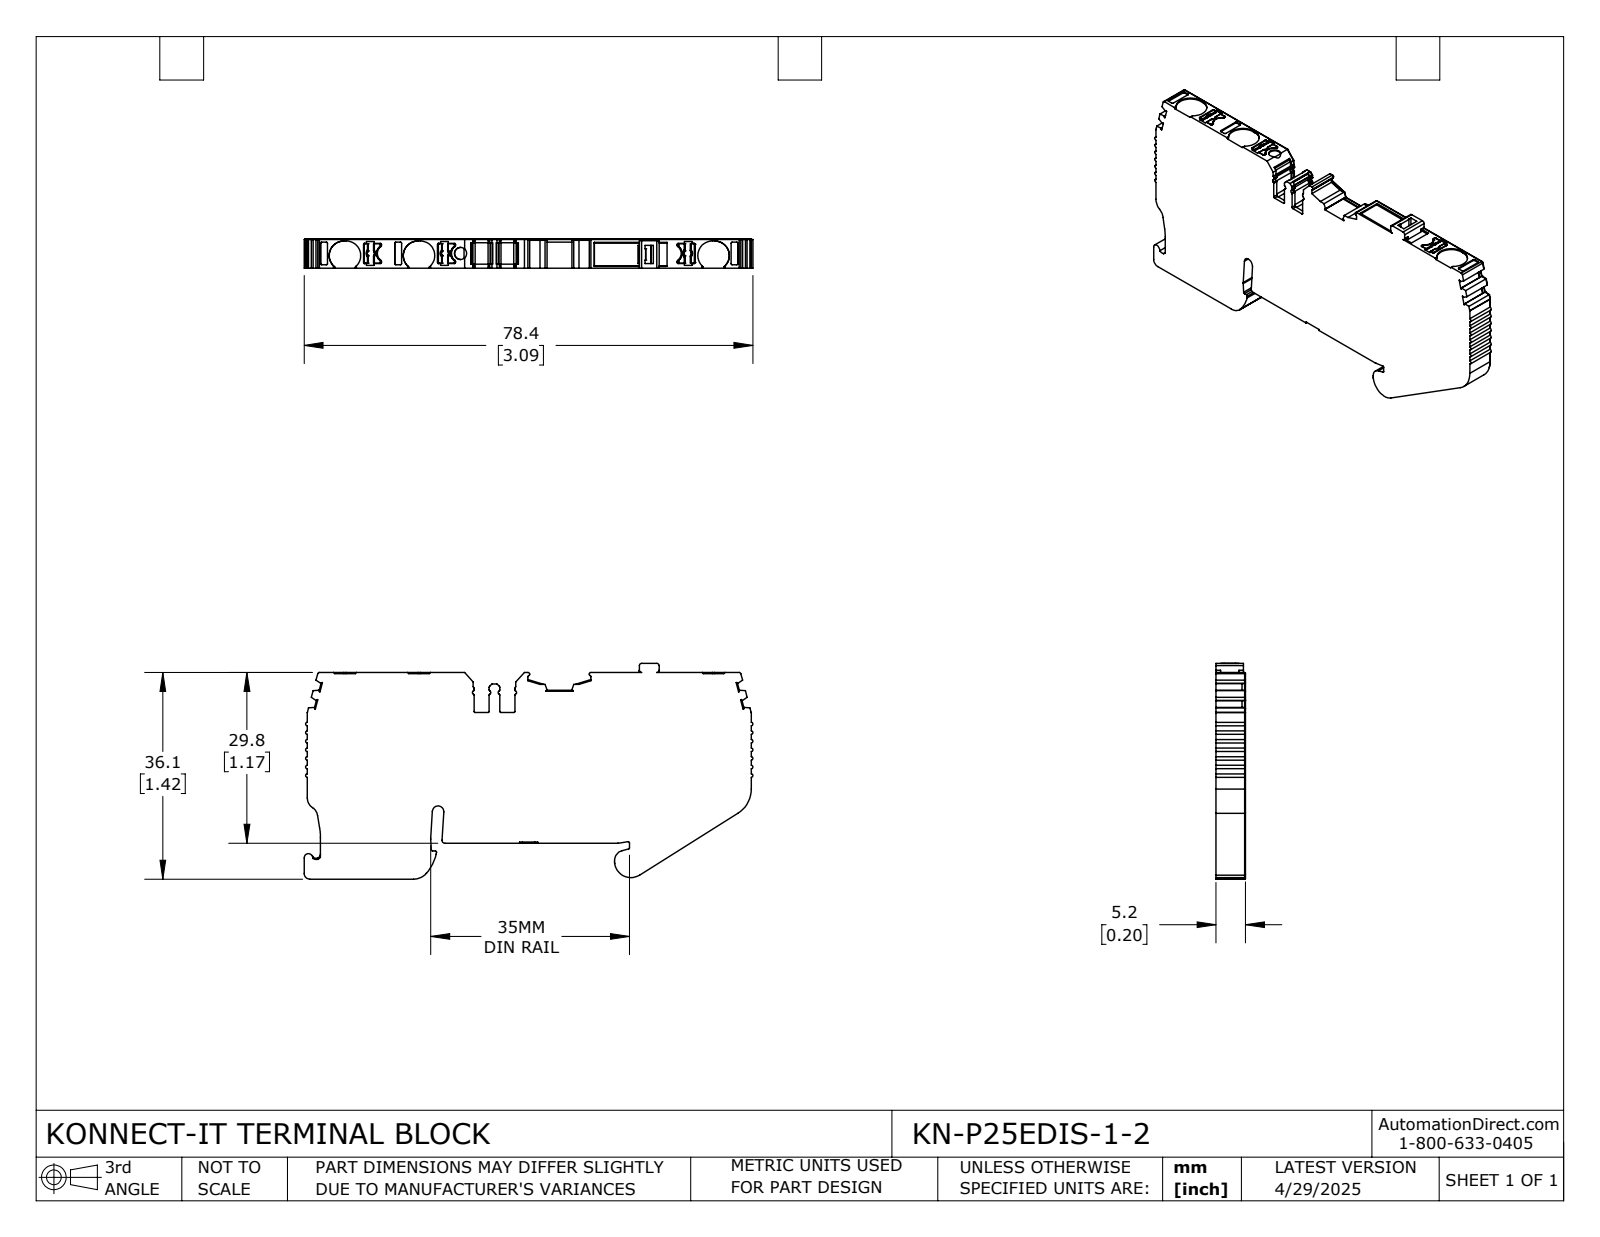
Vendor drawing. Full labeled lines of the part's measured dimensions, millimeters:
Part name (STEP PRODUCT): KN-P25EDIS-1-2
STEP written by: SolidWorks 2024 (CONFIG_CONTROL_DESIGN)
Units: millimetres
Bodies: 1 solid, 691 faces (368 planar, 272 cylindrical, 51 other)
Overall size (bounding box): 78.36 × 37.67 × 5.15
Volume: 11 990 mm³ · Surface area: 6 259 mm²
Round holes (diameter × count): ⌀2.1 ×1
Partial cylindrical surfaces — rounded edges, fillets, slot ends (radius × count): R0.2 ×66, R0.3 ×39, R0.1 ×19, R0.5 ×18, R0.4 ×13, R0.15 ×12, R2.55 ×6, R1 ×4
Main face-to-face distances: 5.15, 29.61, 29.81, 6.26, 35.87, 36.07, 77.52, 1.2, 5, 4.5
